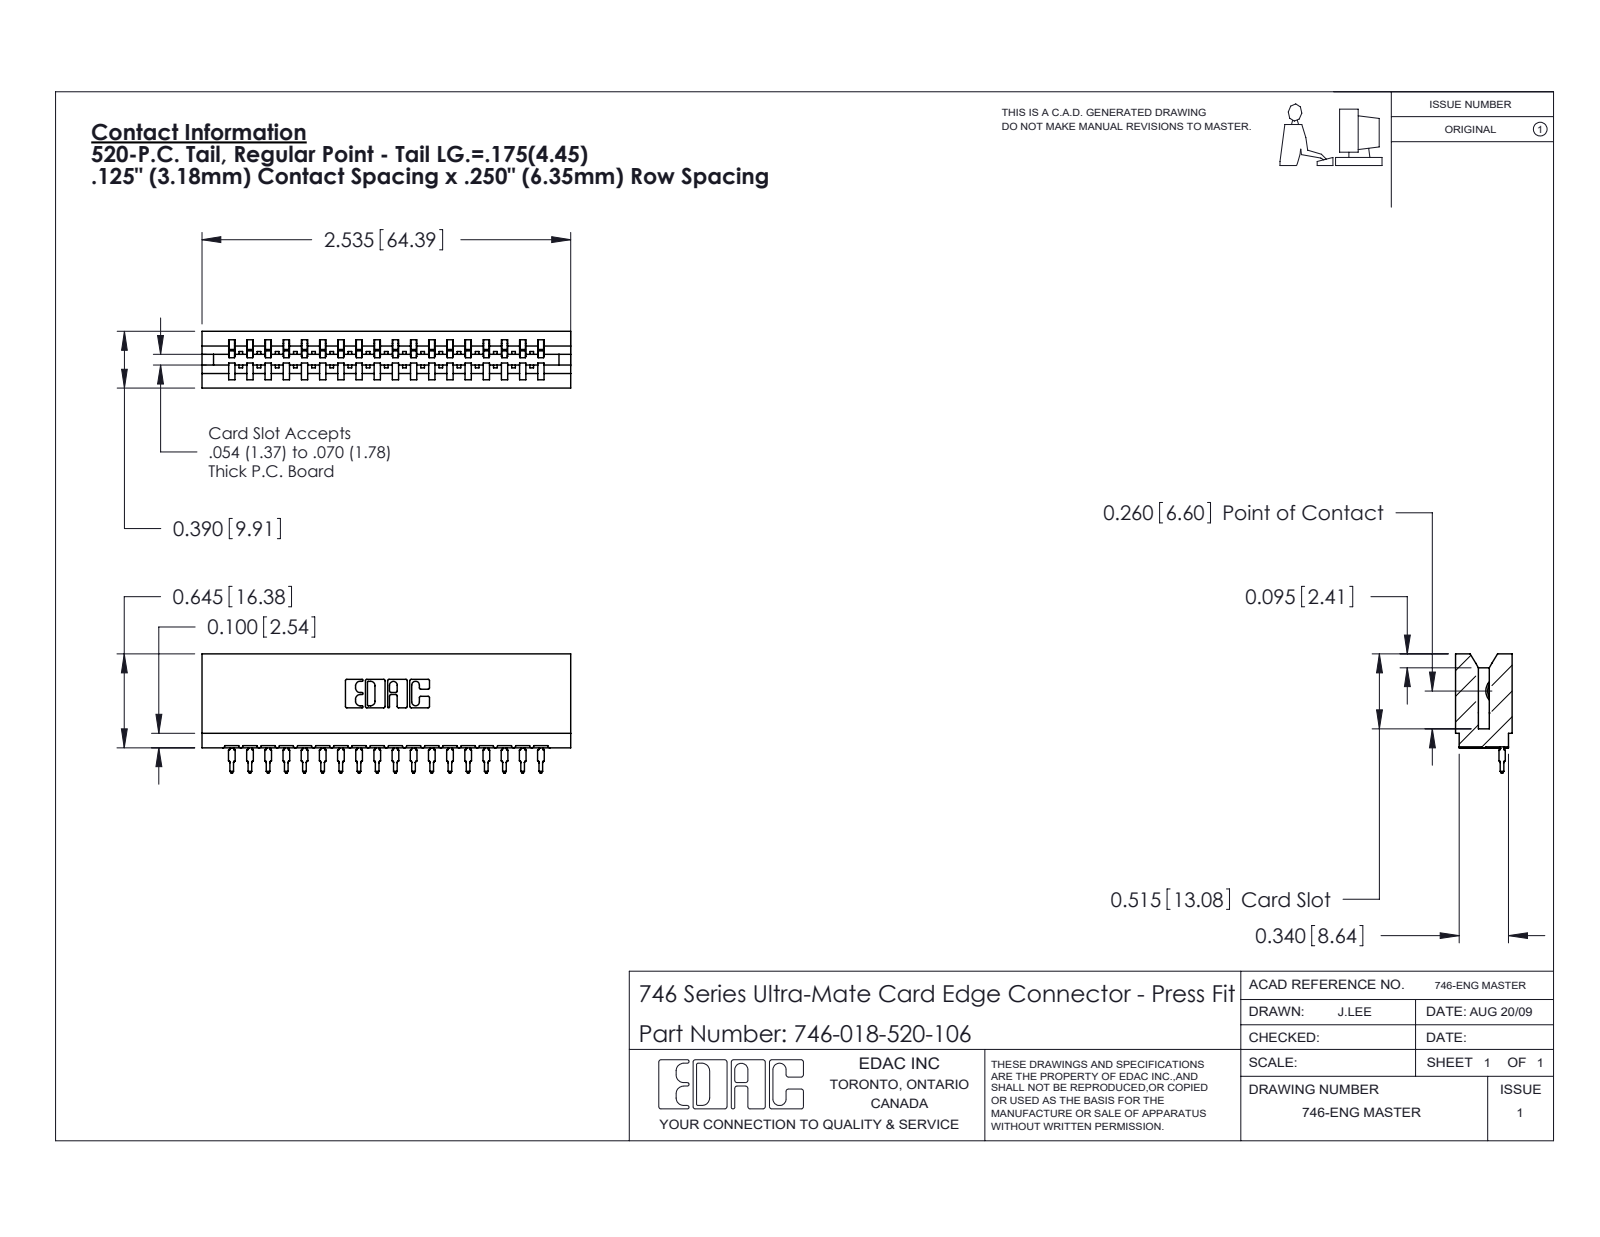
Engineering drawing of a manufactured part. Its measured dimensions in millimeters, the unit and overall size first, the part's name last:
Units: millimetres
Overall size (bounding box): 64.4 × 20.8 × 9.9
Partial cylindrical surfaces — rounded edges, fillets, slot ends (radius × count): R0.5 ×36, R0.3 ×22, R0.4 ×19, R0.2 ×6, R0.8 ×6, R0.1 ×4, R0.3 ×4, R0.7 ×3
Main face-to-face distances: 6.4, 8.5, 1.4, 9.9, 12.7, 3.2, 3.2, 1.1, 5.3, 11.6
Volume: 6 830 mm³ · Surface area: 9 626 mm²
Bodies: 19 solids, 2042 faces (1190 planar, 384 cylindrical, 468 other)
Part name (STEP PRODUCT): 746-292-001_520; 746 Part_.515 Slot Depth - 06; 746-018-520-106
STEP written by: SolidWorks 2020 (CONFIG_CONTROL_DESIGN)
